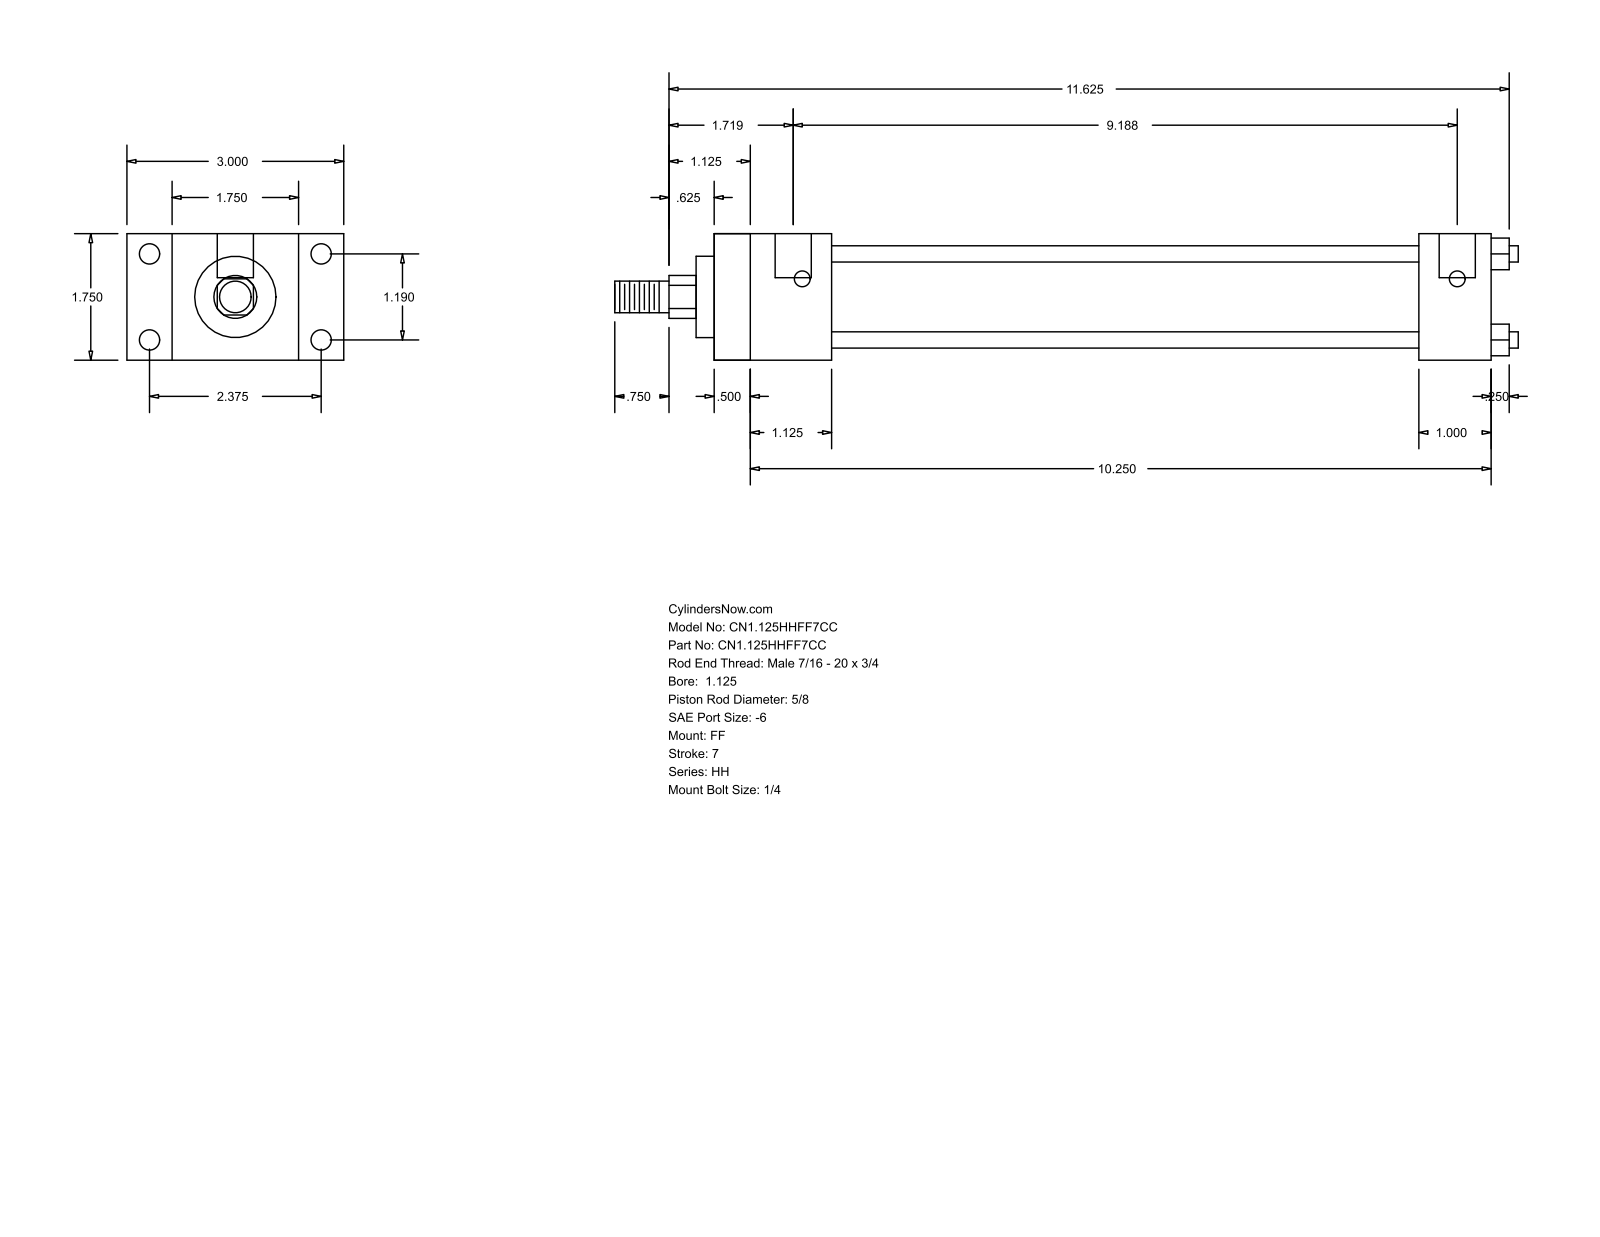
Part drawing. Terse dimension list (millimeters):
name: HH_FF__0112_0.625
written by: GSSL Pune (CONFIG_CONTROL_DESIGN)
unit: mm
bodies: 0 solids, 92 faces (64 planar, 28 cylindrical, 0 other)
size: 317.5 × 76.2 × 44.45
holes: 4× ⌀5.56, 4× ⌀7.14, 2× ⌀12.7
bosses: 4× ⌀5.71, 1× ⌀34.92, 1× ⌀28.57, 1× ⌀15.88, 1× ⌀11.11
rounds: 1× R7.54
face distances: 44.46, 273.05, 12.69, 260.36, 15.87, 28.58, 60.33, 41.27, 247.64, 234.95
hole spacings: 30.22, 60.32, 67.47, 230.19, 3.17, 233.36
